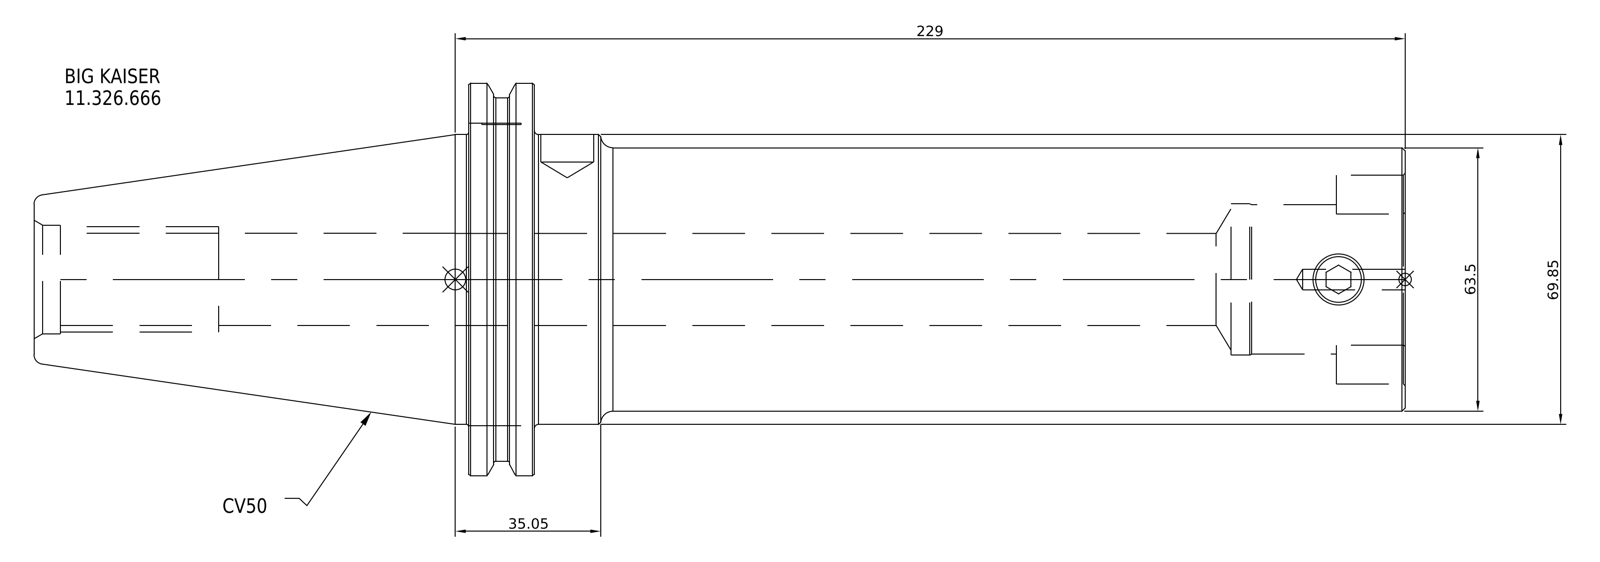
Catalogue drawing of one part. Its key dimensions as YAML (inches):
part_name: "11.326.666"
step_written_by: "SolidWorks 2021 (CONFIG_CONTROL_DESIGN)"
units: inches
bodies: {solids: 1, faces: 16, planar: 7, cylindrical: 6, other: 3}
overall_size: [13.016, 3.875, 3.875]
volume: 64.2
surface_area: 123.3
round_bosses_or_shafts:
  - {diameter: 3.875, count: 1}
  - {diameter: 3.594, count: 1}
  - {diameter: 2.75, count: 1}
  - {diameter: 2.491, count: 1}
face_to_face_distances: [0.691, 8.266, 8.957, 13.016, 4.75, 4.059, 7.638, 0.628, 1.319, 5.378]
